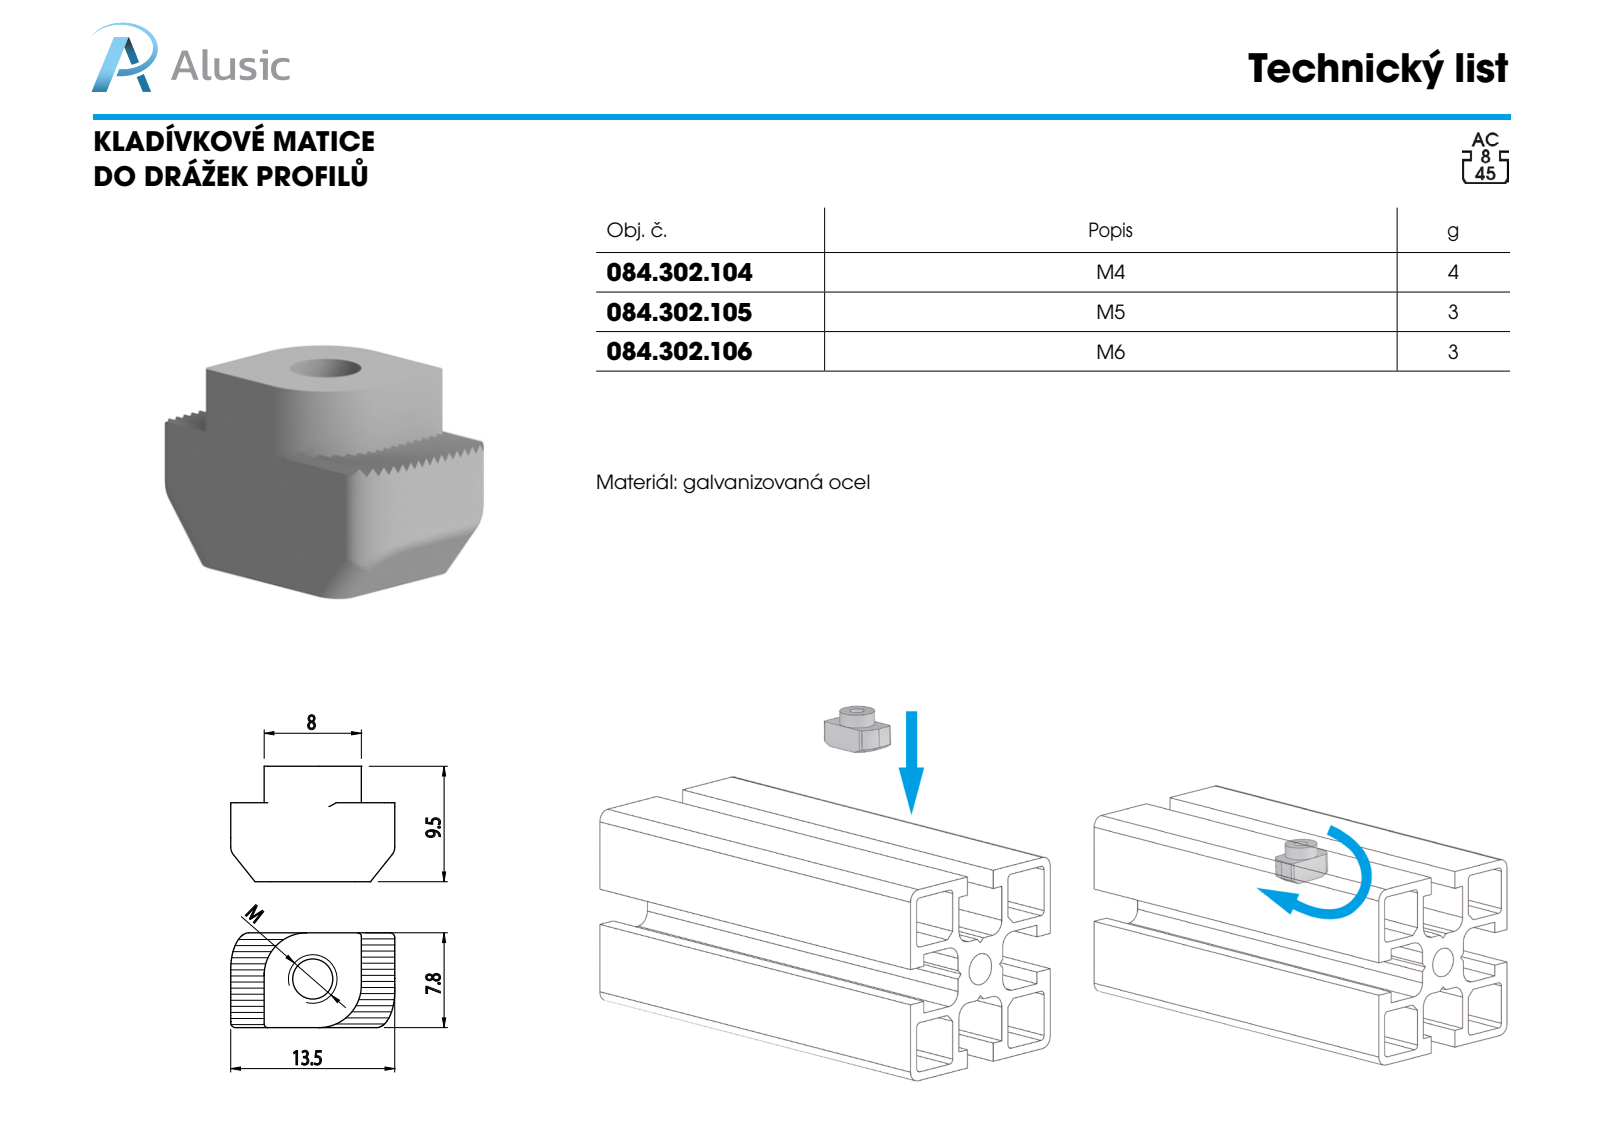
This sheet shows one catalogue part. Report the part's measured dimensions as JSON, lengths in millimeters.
{"part_name": "084.302.105", "step_written_by": "SolidWorks 2016 (CONFIG_CONTROL_DESIGN)", "units": "millimeters", "bodies": {"solids": 1, "faces": 22, "planar": 10, "cylindrical": 10, "other": 2}, "overall_size": [14, 8.5, 8], "volume_mm3": 604, "surface_area_mm2": 581, "round_holes": [[4.2, 1]], "round_bosses_or_shafts": [[8, 1]], "partial_cylinders_radius": [[0.5, 2], [1, 2], [5, 2]], "face_to_face_distances": [8, 5.5, 8.5, 3, 14]}
